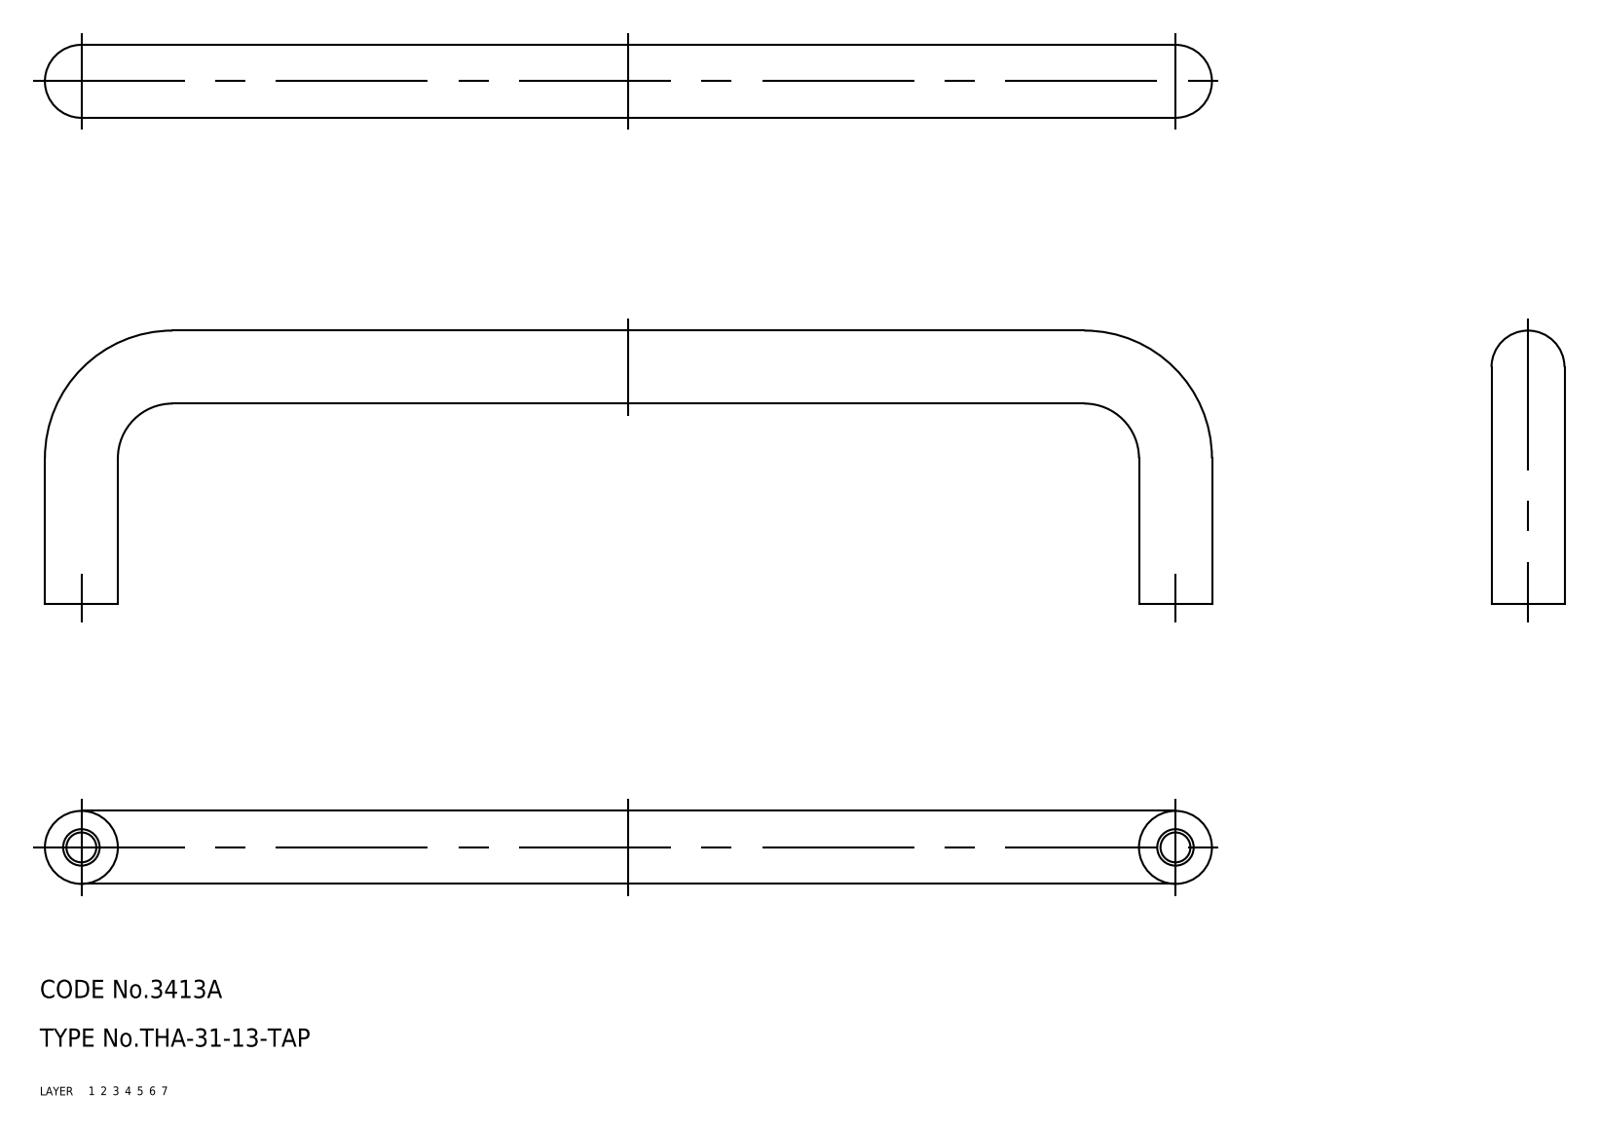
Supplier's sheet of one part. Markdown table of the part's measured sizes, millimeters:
| quantity | value |
| --- | --- |
| part name | pull |
| STEP written by | CADfix (AUTOMOTIVE_DESIGN) |
| units | millimeters |
| bodies | 1 solid, 18 faces (0 planar, 0 cylindrical, 18 other) |
| overall size | 192 × 45 × 12 |
| volume | 26 695 mm³ |
| surface area | 10 227 mm² |
